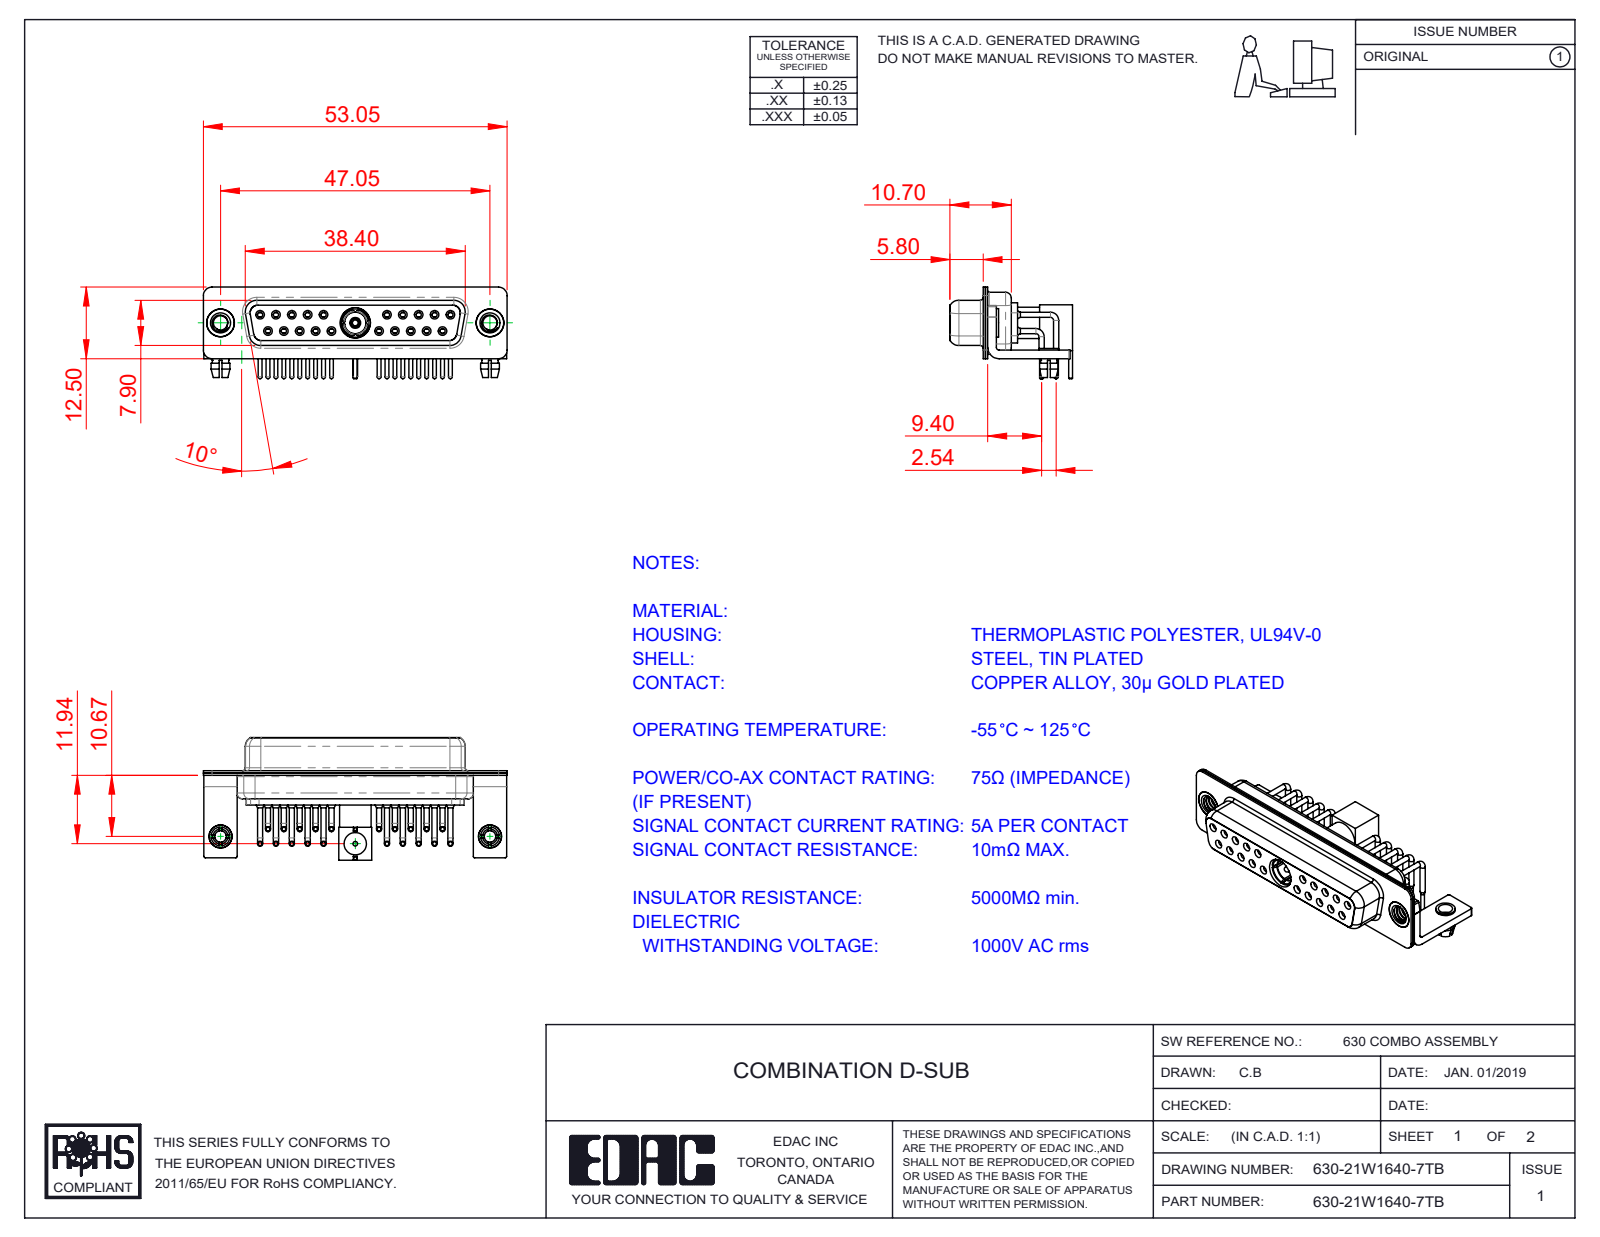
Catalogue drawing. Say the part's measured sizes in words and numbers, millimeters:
The part is named "630Combo Stabilizer Bracket; Pin_RA; 630Combo Housing_21W1; Co-Ax Plug Assy_RA (+8 more)". Its 3-D file was written by "SolidWorks 2020 (CONFIG_CONTROL_DESIGN)". It is 35 solids with 1637 faces: 502 planar, 712 cylindrical and 423 other. Overall it measures 53.05 by 21.41 by 16 millimeters. Its volume is 4 490 cubic millimeters and its surface area 10 770 square millimeters. Round holes: 22 of diameter 2, 21 of diameter 1.1, 21 of diameter 1.5, 20 of diameter 0.9, 10 of diameter 1.6, 10 of diameter 1.7, 4 of diameter 2.5, 3 of diameter 4.85, 2 of diameter 3.2, 2 of diameter 4, 2 of diameter 4.05, 1 of diameter 0.8. Round bosses or shafts: 20 of diameter 0.9, 20 of diameter 0.65, 10 of diameter 1.6, 3 of diameter 5, 3 of diameter 4, 3 of diameter 2.9, 2 of diameter 4.95, 2 of diameter 4.8. Partial cylindrical surfaces (rounded edges, fillets, slot ends): 16 of radius 0.25, 16 of radius 1.5, 13 of radius 2, 8 of radius 1.35, 8 of radius 1.6, 5 of radius 0.5, 4 of radius 0.6, 4 of radius 0.65. The main face-to-face distances are 0.4, 0.45, 1.4, 8.45, 1.8, 0.8, 8.9, 6.2, 7.05, 1.35. The hole center spacings are 3.16, 2.77, 5.54, 8.31, 5.04, 19.39, 20.97, 22.16.
